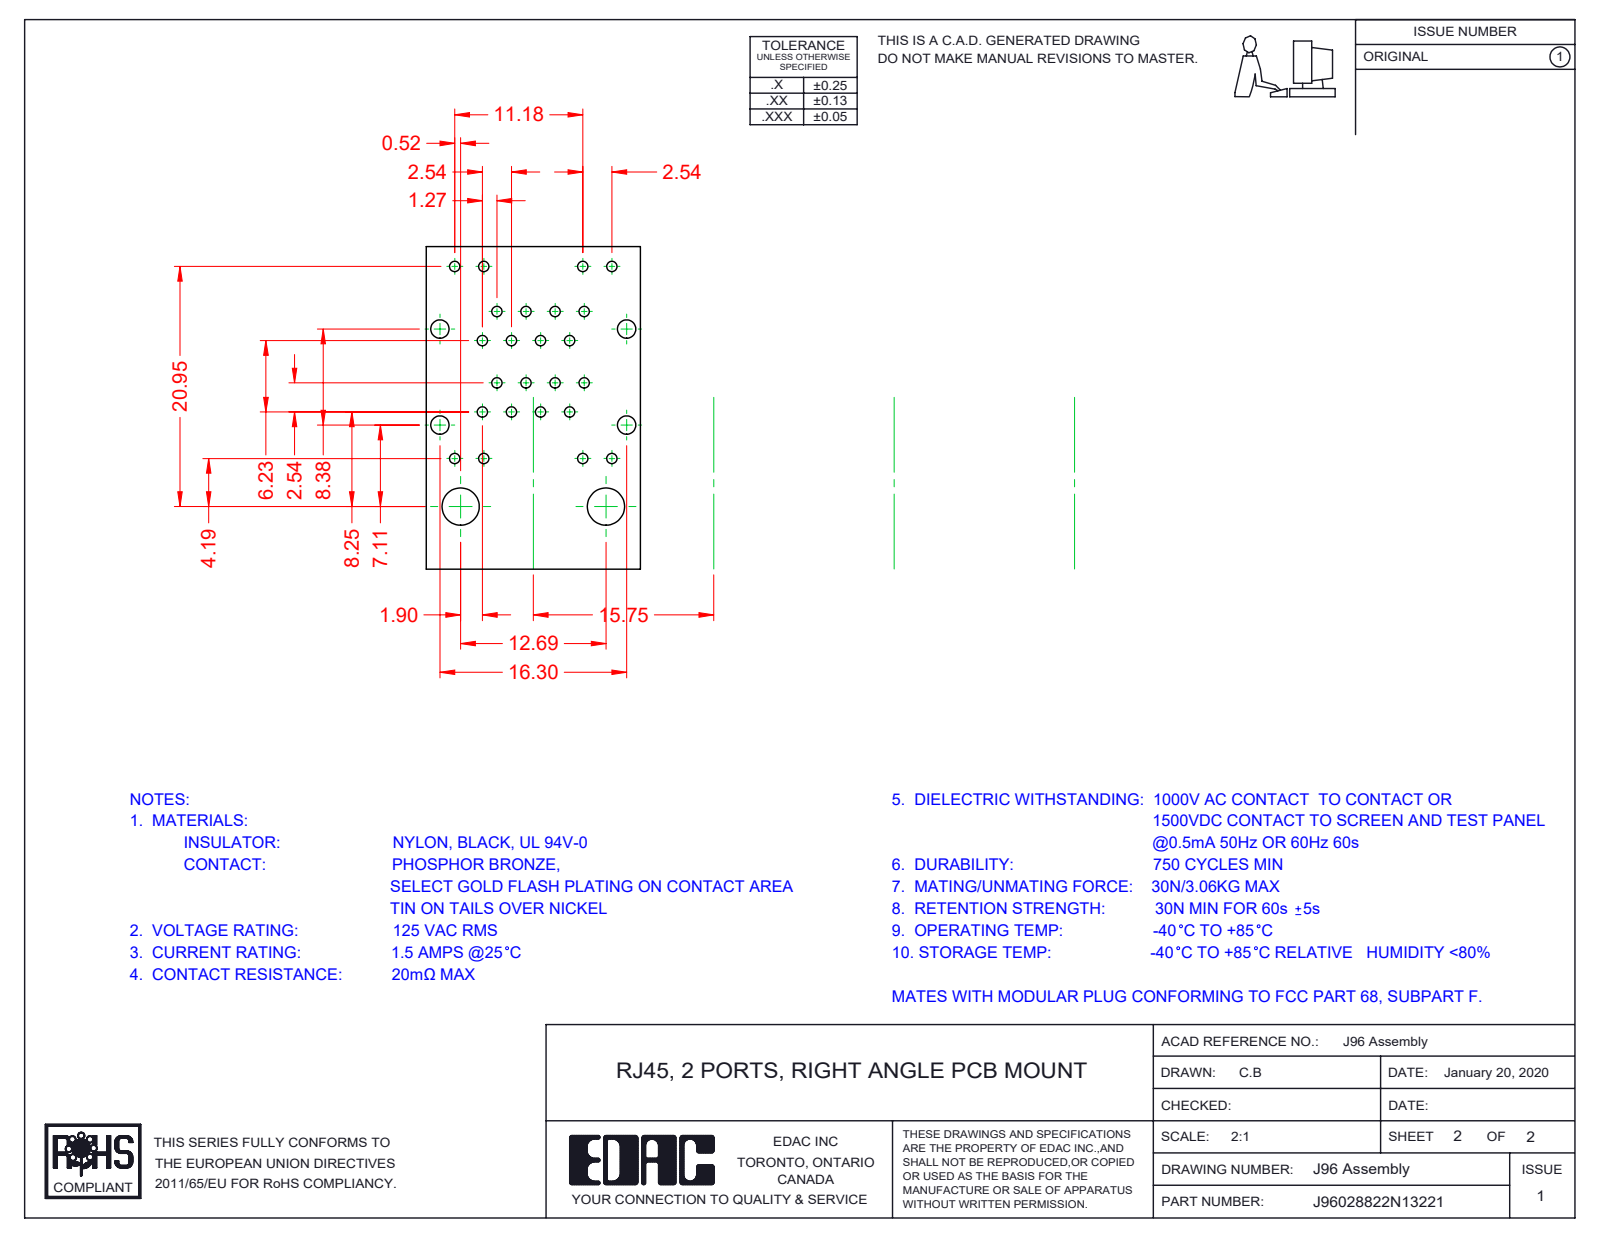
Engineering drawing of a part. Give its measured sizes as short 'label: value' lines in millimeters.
name: 96 Contact Lock Lower; 96 Contacts Lower; 96 Contacts Upper; 96 LED RH Lower_3-Green (+8 more)
written by: SolidWorks 2016 (CONFIG_CONTROL_DESIGN)
unit: mm
bodies: 27 solids, 2417 faces (1865 planar, 446 cylindrical, 106 other)
size: 31.38 × 28.68 × 16.8
volume: 6 849 mm³; area: 19 094 mm²
rounds: 48× R0.25, 32× R0.15, 24× R0.35, 16× R0.5, 16× R1, 14× R0.2, 9× R0.7, 5× R2
face distances: 16.3, 16.1, 1.75, 16.5, 14.75, 1.55, 14.55, 0.53, 1.48, 11.2
